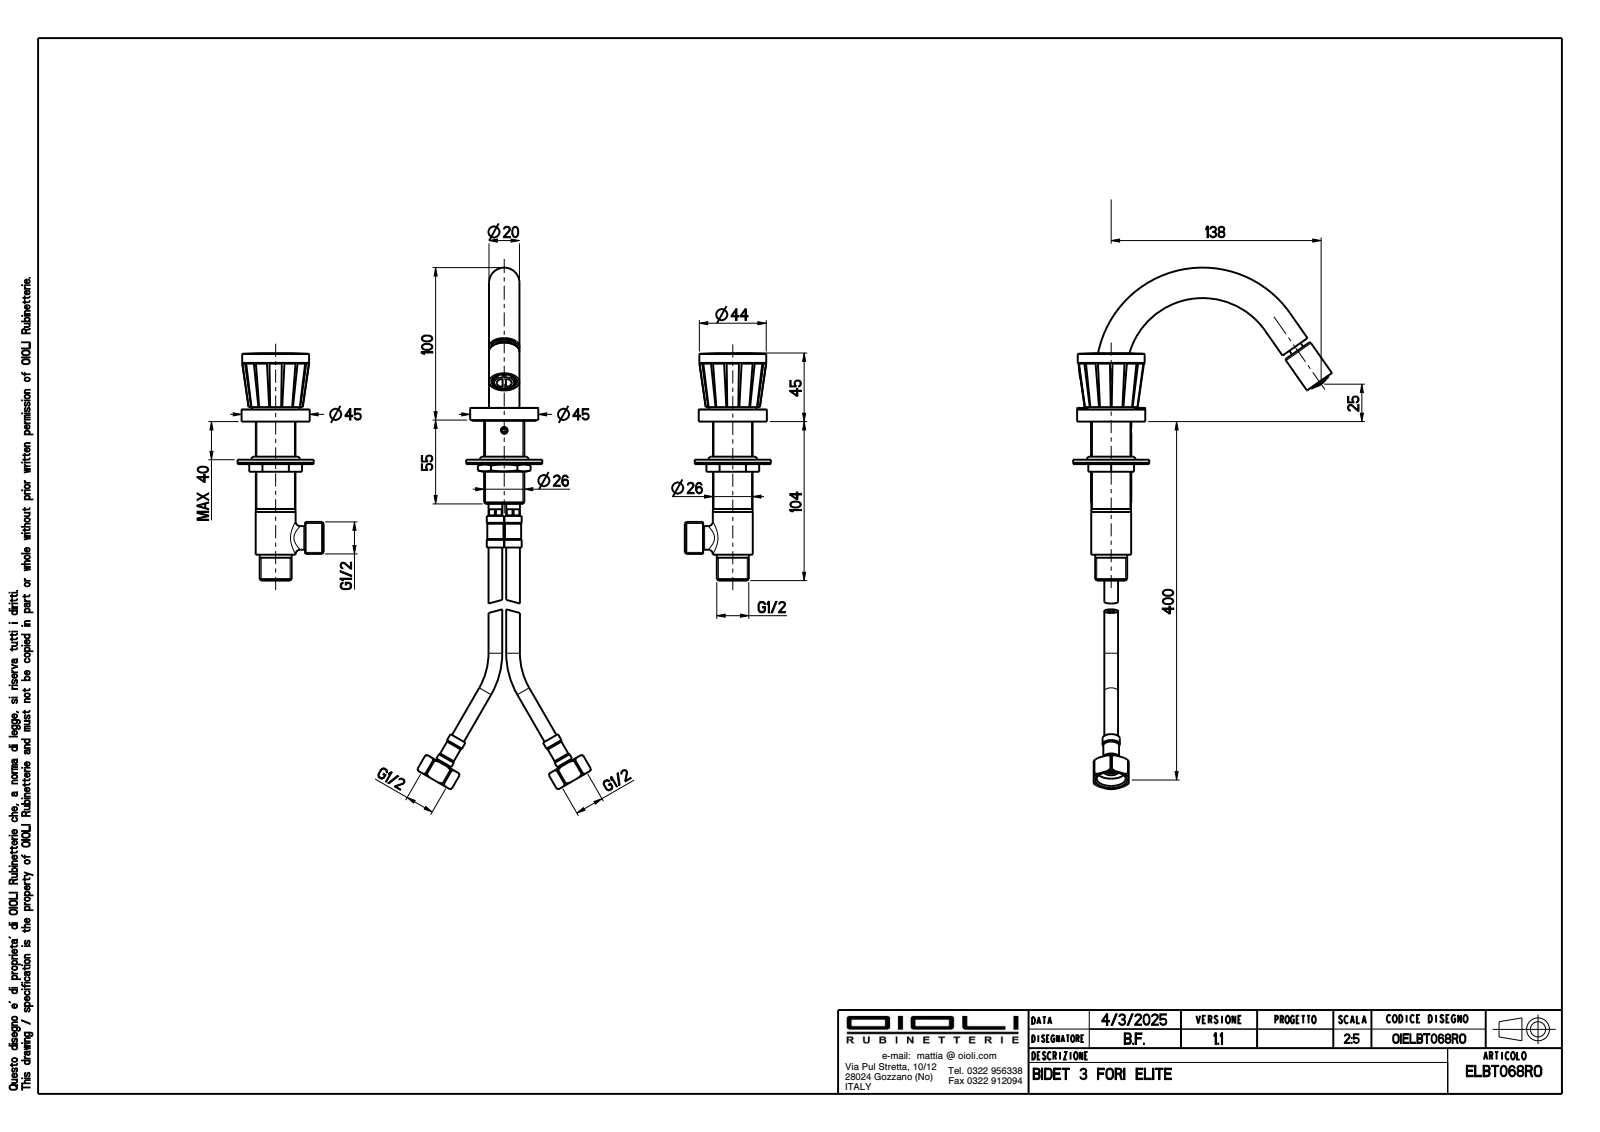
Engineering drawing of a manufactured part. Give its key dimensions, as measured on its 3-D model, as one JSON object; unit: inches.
{"part_name": "OIBR00323; OICT00048; OIAR00062; OIAR00046 (+4 more)", "step_written_by": "CREO PARAMETRIC BY PTC INC, 2024493 (CONFIG_CONTROL_DESIGN)", "units": "inches", "bodies": {"solids": 11, "faces": 1244, "planar": 734, "cylindrical": 215, "other": 295}, "overall_size": [13.571, 6.58, 3.976], "volume_in3": 6.04, "surface_area_in2": 107.1, "round_holes": [[1.654, 3], [0.157, 2], [0.165, 2], [0.209, 2], [0.256, 2], [0.276, 2], [0.591, 2], [0.61, 2], [0.659, 2], [0.972, 2], [1.299, 2], [0.573, 1]], "round_bosses_or_shafts": [[0.65, 5], [1.76, 3], [1.437, 3], [0.787, 3], [1.728, 2], [1.22, 2], [1.024, 2], [0.646, 2]], "partial_cylinders_radius": [[0.004, 22], [0.035, 8], [0.024, 4], [0.018, 3], [0.098, 1], [0.128, 1], [0.265, 1], [0.294, 1]], "face_to_face_distances": [0.039, 0.315, 1.339, 1.654, 0.354, 1.299, 0.083, 0.232, 0.043, 0.276], "hole_center_spacings": [5.906, 11.811]}
